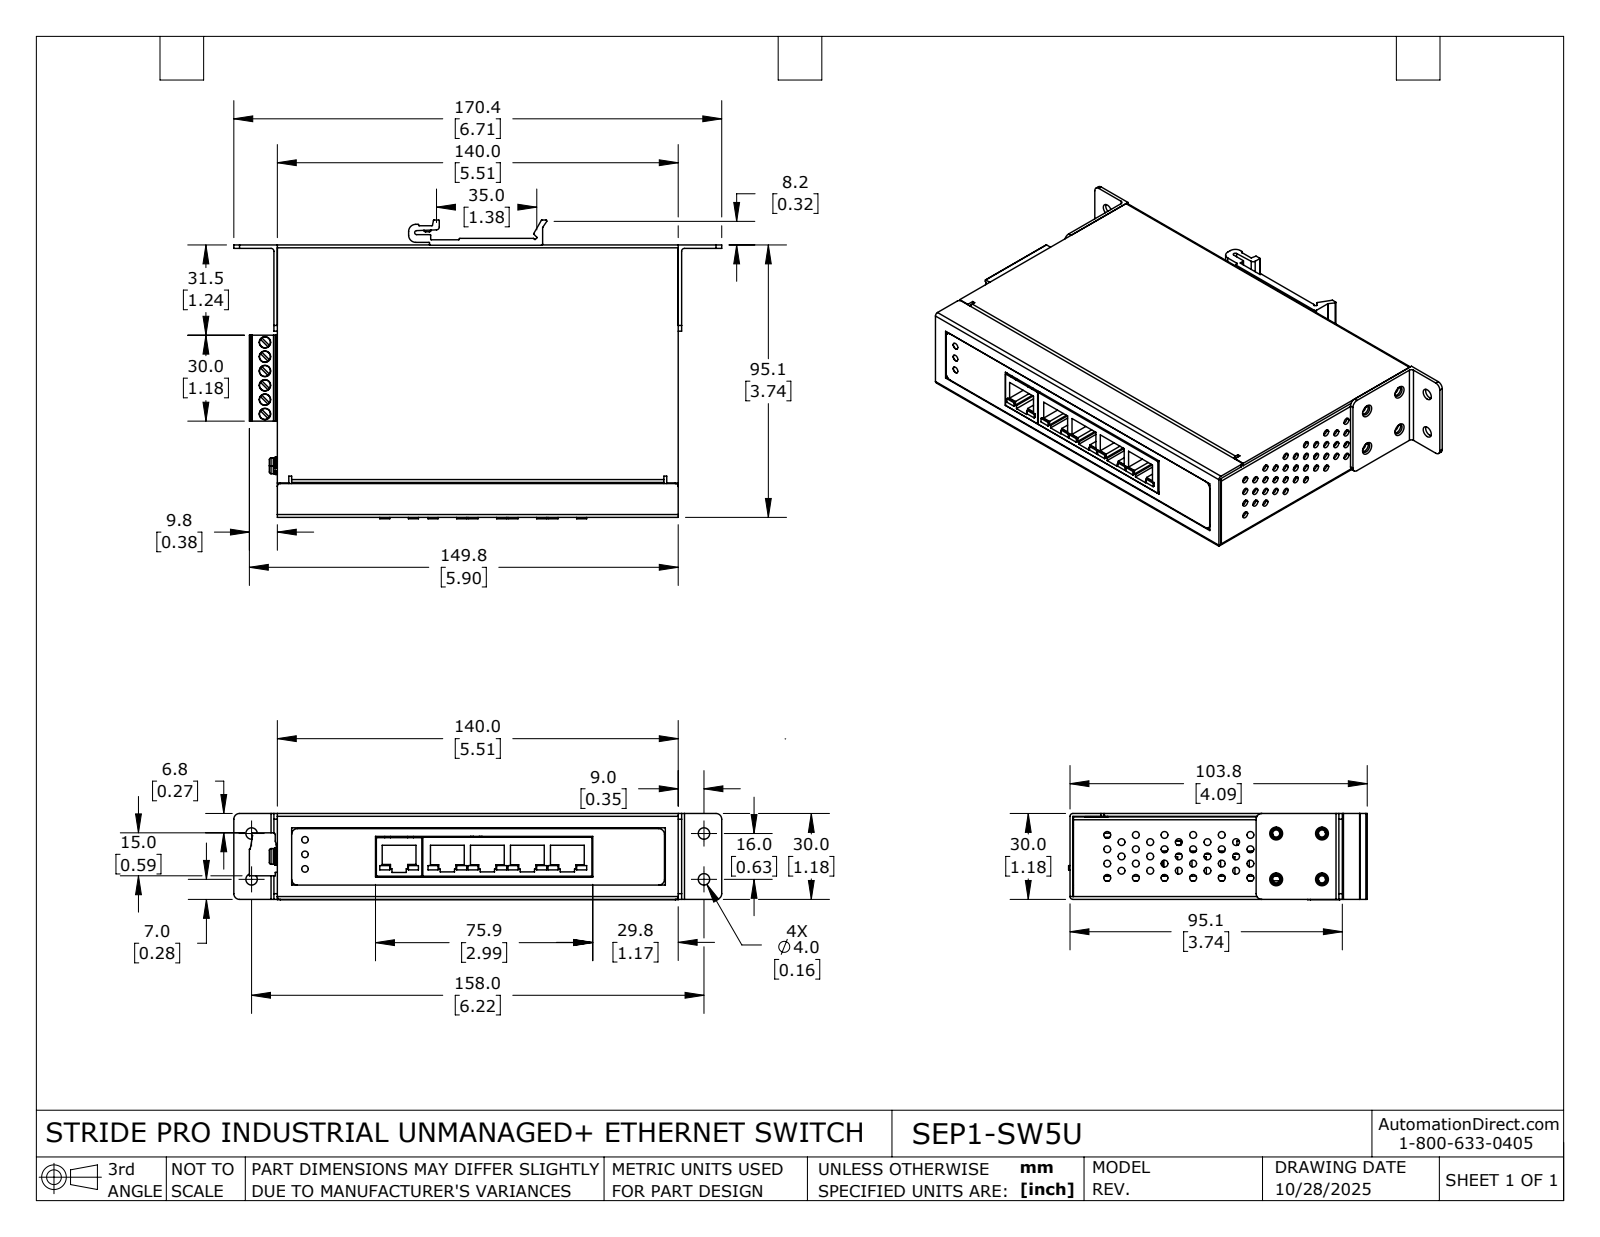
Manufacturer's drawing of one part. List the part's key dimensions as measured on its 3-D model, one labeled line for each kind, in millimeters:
Part name (STEP PRODUCT): SEP1-SW5U
STEP written by: SolidWorks 2024 (AUTOMOTIVE_DESIGN)
Units: millimetres
Bodies: 16 solids, 1912 faces (1011 planar, 698 cylindrical, 203 other)
Overall size (bounding box): 149.8 × 104.3 × 30.1
Volume: 86 620 mm³ · Surface area: 129 400 mm²
Round holes (diameter × count): ⌀2.4 ×51, ⌀2.5 ×11, ⌀4 ×9, ⌀1.4 ×6, ⌀2.8 ×5, ⌀3.2 ×4, ⌀2 ×3, ⌀2.3 ×3, ⌀3 ×3, ⌀3.5 ×2, ⌀1.5 ×1
Round bosses / shafts (diameter × count): ⌀4.1 ×7, ⌀3.8 ×6, ⌀0.5 ×6, ⌀5 ×5, ⌀3 ×5, ⌀5.4 ×4, ⌀4 ×3, ⌀5.5 ×1
Partial cylindrical surfaces — rounded edges, fillets, slot ends (radius × count): R0.1 ×79, R0.2 ×29, R1 ×27, R0.3 ×20, R0.5 ×13, R2 ×11, R0.2 ×10, R0.9 ×6
Main face-to-face distances: 1, 29, 0.5, 28, 20.9, 21.9, 1.6, 22.5, 23.5, 7.1
Hole centre spacings: 10, 11.2, 5, 20.6, 14.1, 20, 30.4, 22.4
